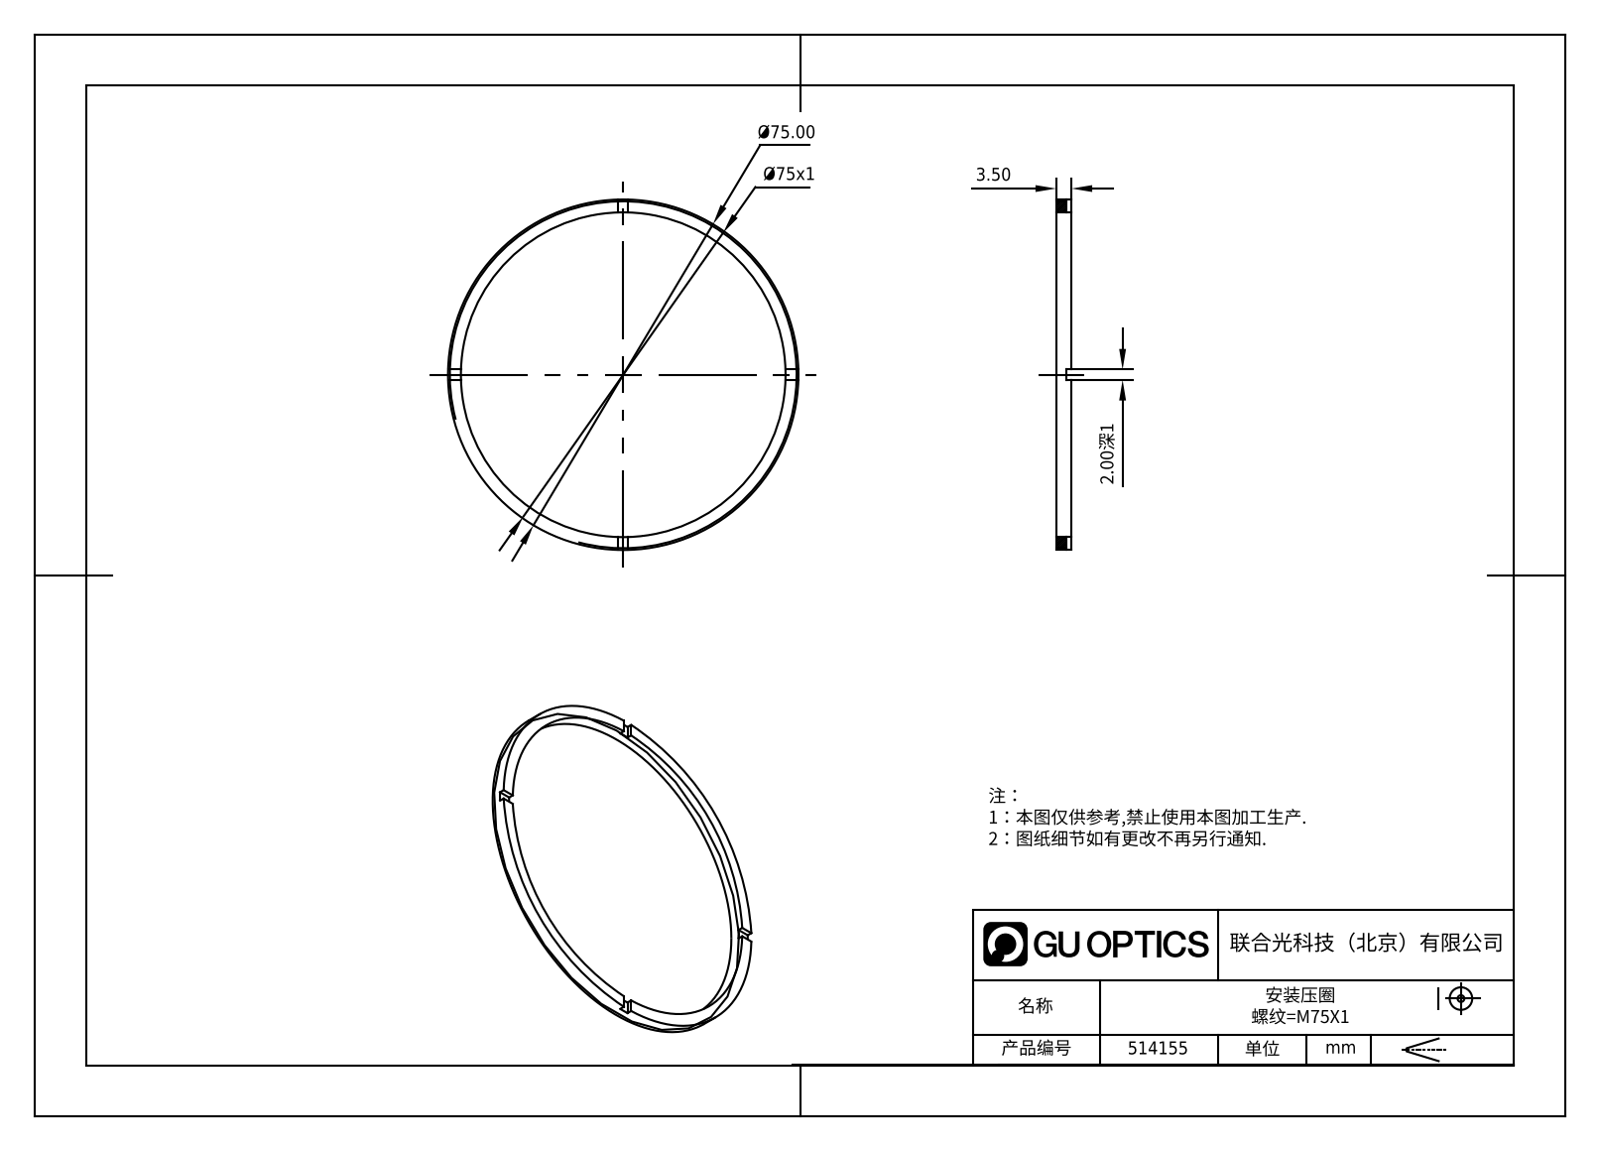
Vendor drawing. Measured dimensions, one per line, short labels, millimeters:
name: 514155
written by: SolidWorks 2020 (CONFIG_CONTROL_DESIGN)
unit: mm
bodies: 1 solid, 21 faces (17 planar, 4 cylindrical, 0 other)
size: 75 × 75 × 3.5
volume: 2 351 mm³; area: 2 949 mm²
holes: 1× ⌀69
bosses: 1× ⌀75
face distances: 3.5, 2.5, 1, 2
